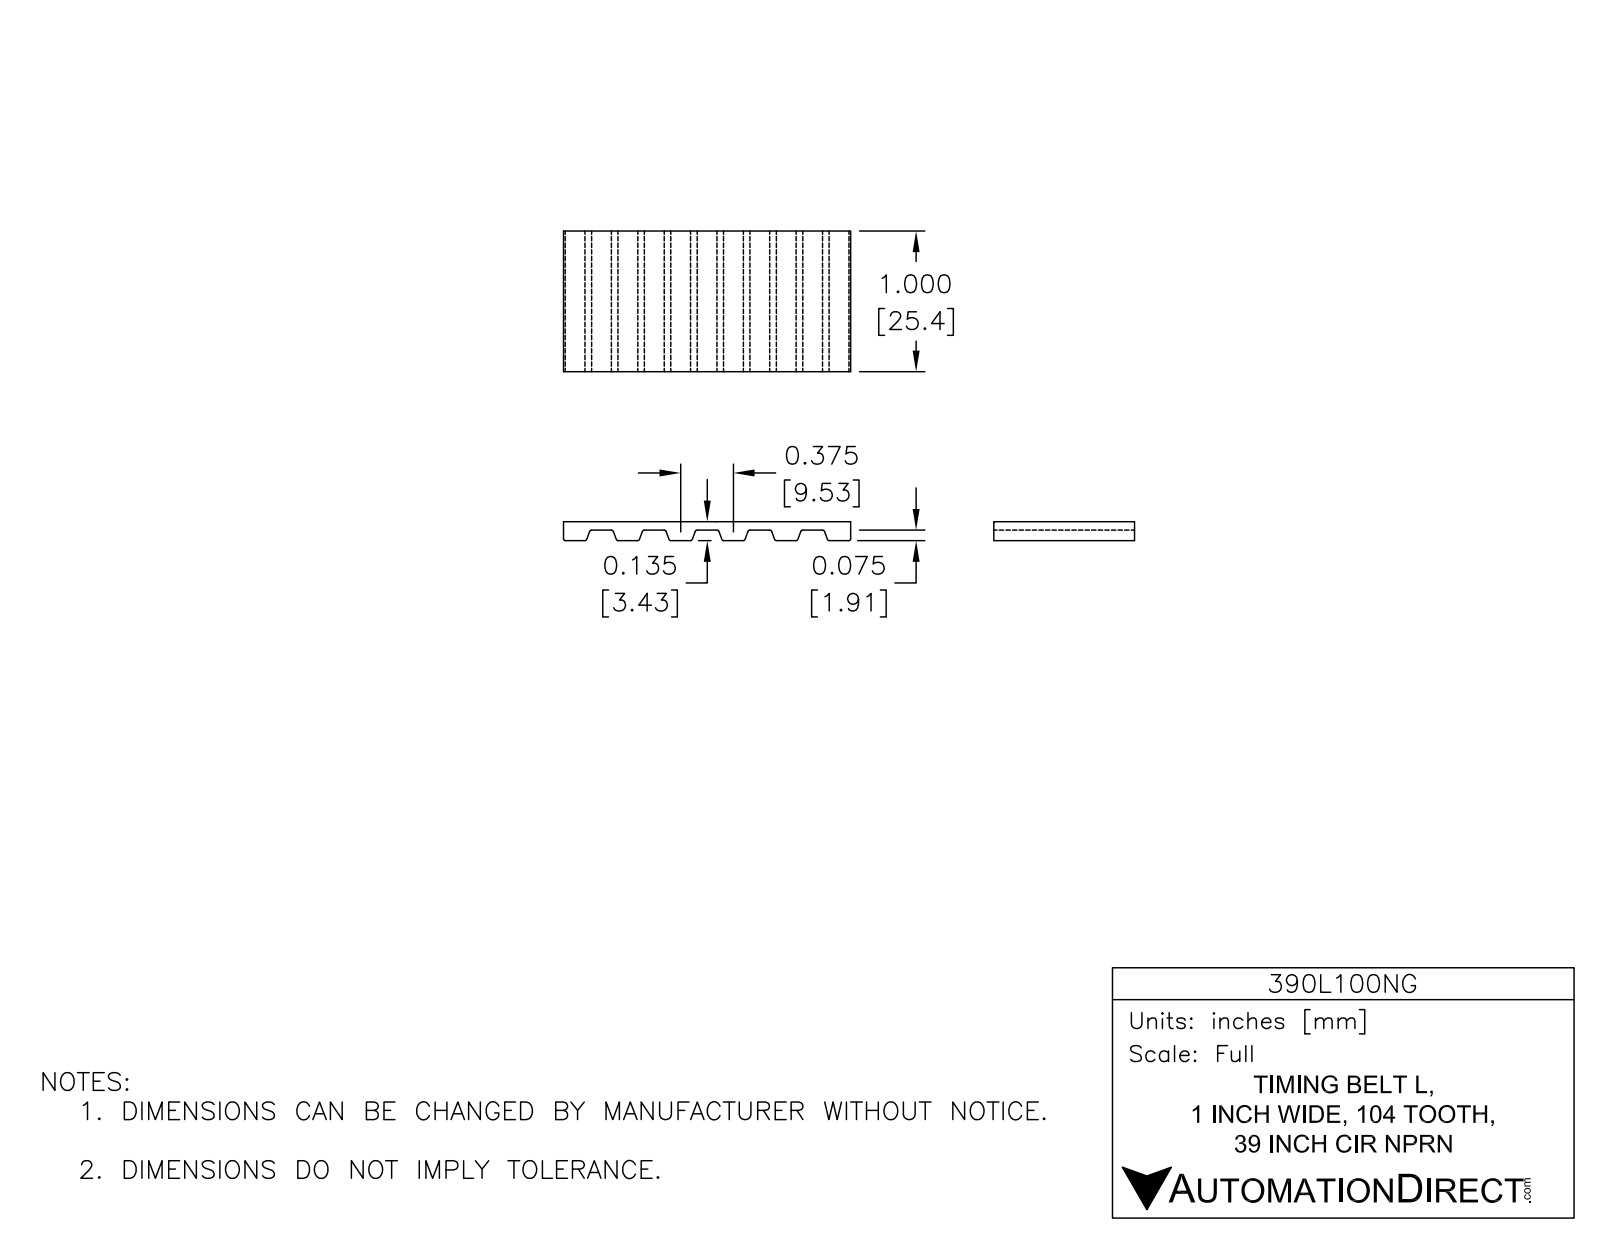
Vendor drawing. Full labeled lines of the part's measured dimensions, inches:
Part name (STEP PRODUCT): 390L100NG
STEP written by: SolidWorks 2014 (AUTOMOTIVE_DESIGN)
Units: inches
Bodies: 1 solid, 847 faces (393 planar, 454 cylindrical, 0 other)
Overall size (bounding box): 17.788 × 3 × 1
Volume: 3.535 in³ · Surface area: 93.99 in²
Partial cylindrical surfaces — rounded edges, fillets, slot ends (radius × count): R0.02 ×412, R1.435 ×2, R1.5 ×2
Main face-to-face distances: 0.065, 2.935, 3, 2.87, 0.14, 2.86, 0.075, 2.795, 1, 2.72
